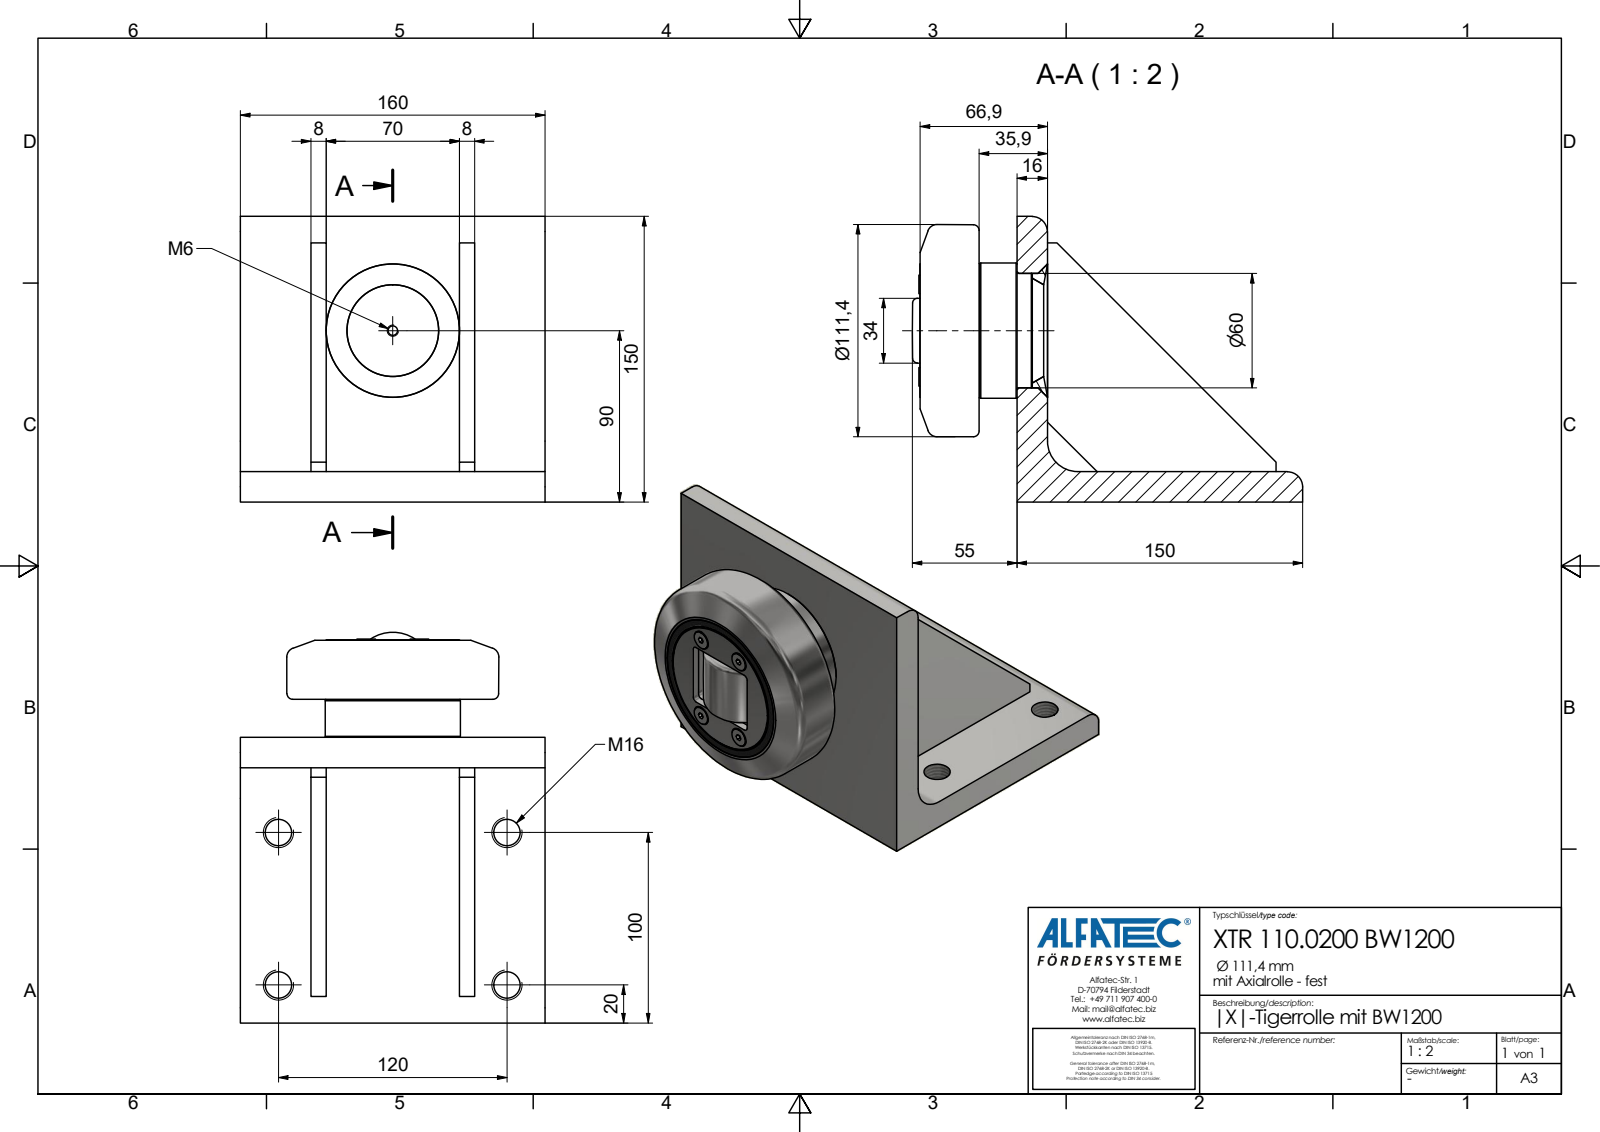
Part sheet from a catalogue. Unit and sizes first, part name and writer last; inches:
Units: inches
Overall size (bounding box): 8.074 × 6.299 × 5.906
Round holes (diameter × count): ⌀0.545 ×4
Round bosses / shafts (diameter × count): ⌀0.384 ×4, ⌀2.795 ×1, ⌀2.776 ×1
Partial cylindrical surfaces — rounded edges, fillets, slot ends (radius × count): R0.079 ×4, R0.315 ×2, R0.63 ×1
Main face-to-face distances: 0.63, 0.315, 3.071, 1.457, 1.772, 4.528, 4.843, 3.386, 2.756, 0.783
Hole centre spacings: 3.15, 4.724, 5.678
Volume: 73.9 in³ · Surface area: 247.6 in²
Bodies: 1 solid, 98 faces (67 planar, 17 cylindrical, 14 other)
Part name (STEP PRODUCT): XTR 110.0200 BW1200_Kontur
STEP written by: Autodesk Inventor 2020 (AP242_MANAGED_MODEL_BASED_3D_ENGINEERING_MIM_LF)
